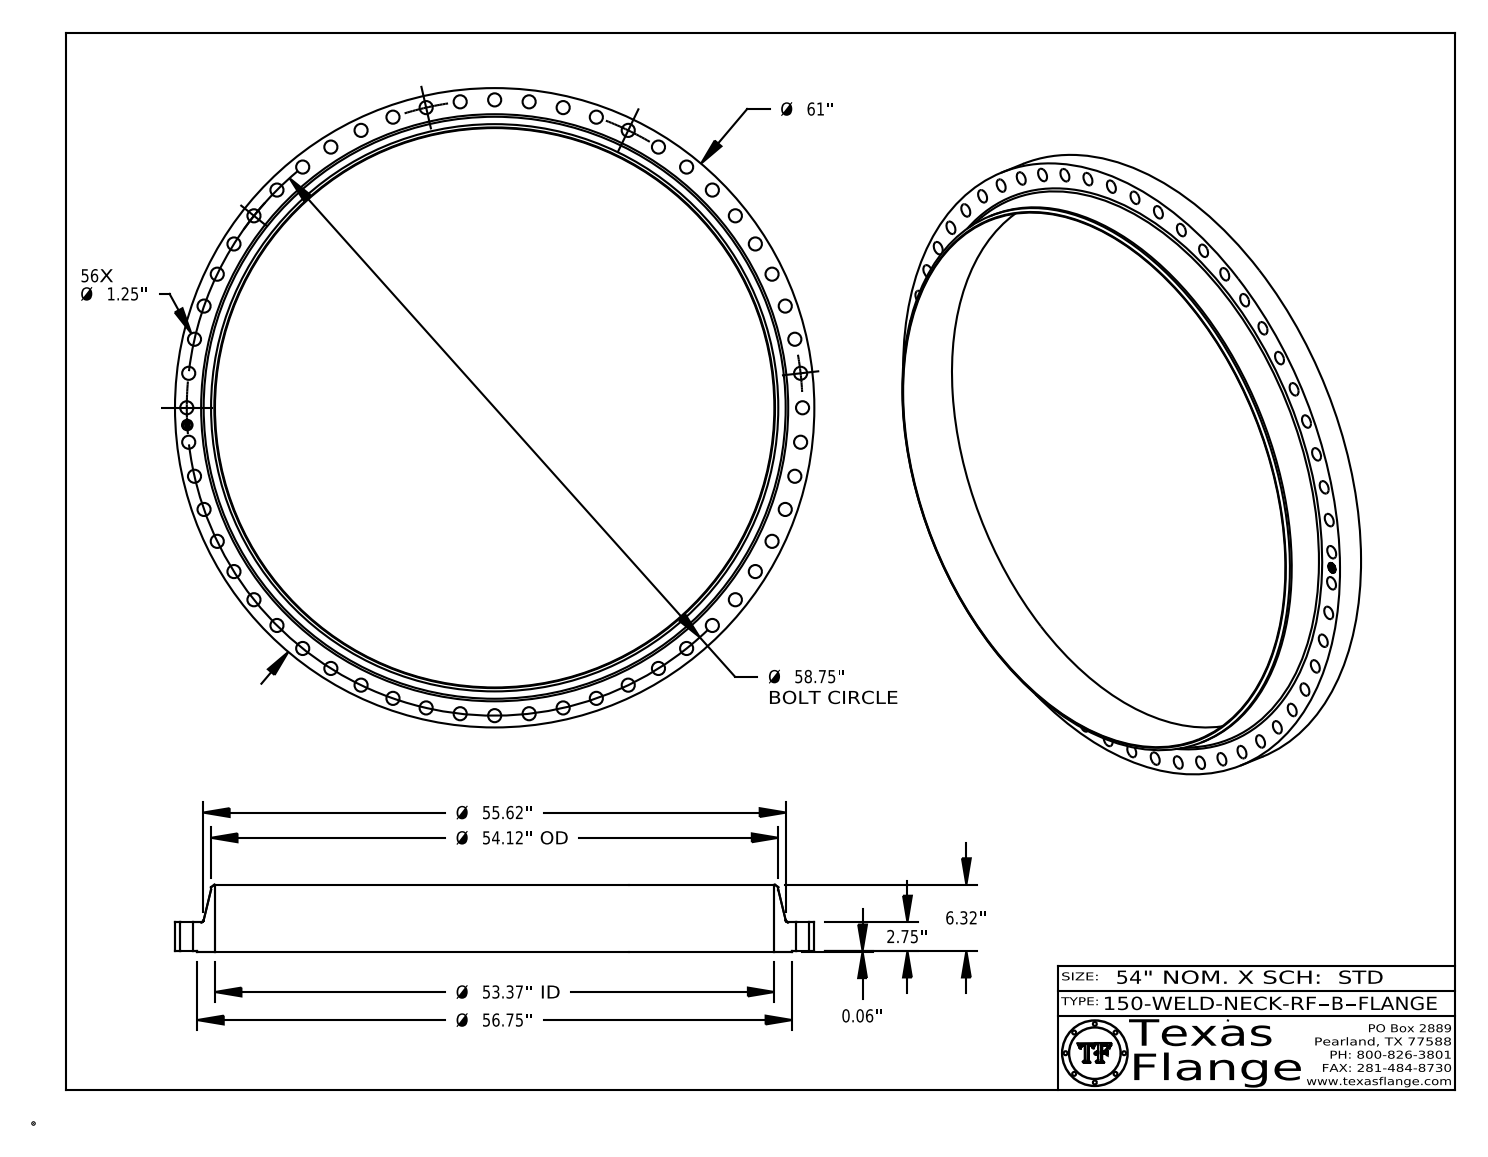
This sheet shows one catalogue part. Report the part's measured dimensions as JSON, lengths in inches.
{"part_name": "150-WELD-NECK-RF, Series B", "step_written_by": "CATIA V5 STEP AP214 (AUTOMOTIVE_DESIGN)", "units": "inches", "bodies": {"solids": 1, "faces": 515, "planar": 369, "cylindrical": 140, "other": 6}, "overall_size": [61, 61, 6.383], "volume_in3": 2134, "surface_area_in2": 3910, "round_holes": [[1.25, 56], [1, 1], [53.37, 1]], "round_bosses_or_shafts": [[0.061, 8], [61, 1], [56.75, 1], [54.12, 1], [0.788, 1]], "face_to_face_distances": [2.75, 0.063, 2.813, 6.383, 6.32, 3.57, 0.015, 2.798, 2.735, 3.585], "hole_center_spacings": [58.657, 3.294, 6.578, 9.841, 29.375, 16.264, 19.404, 13.073]}
